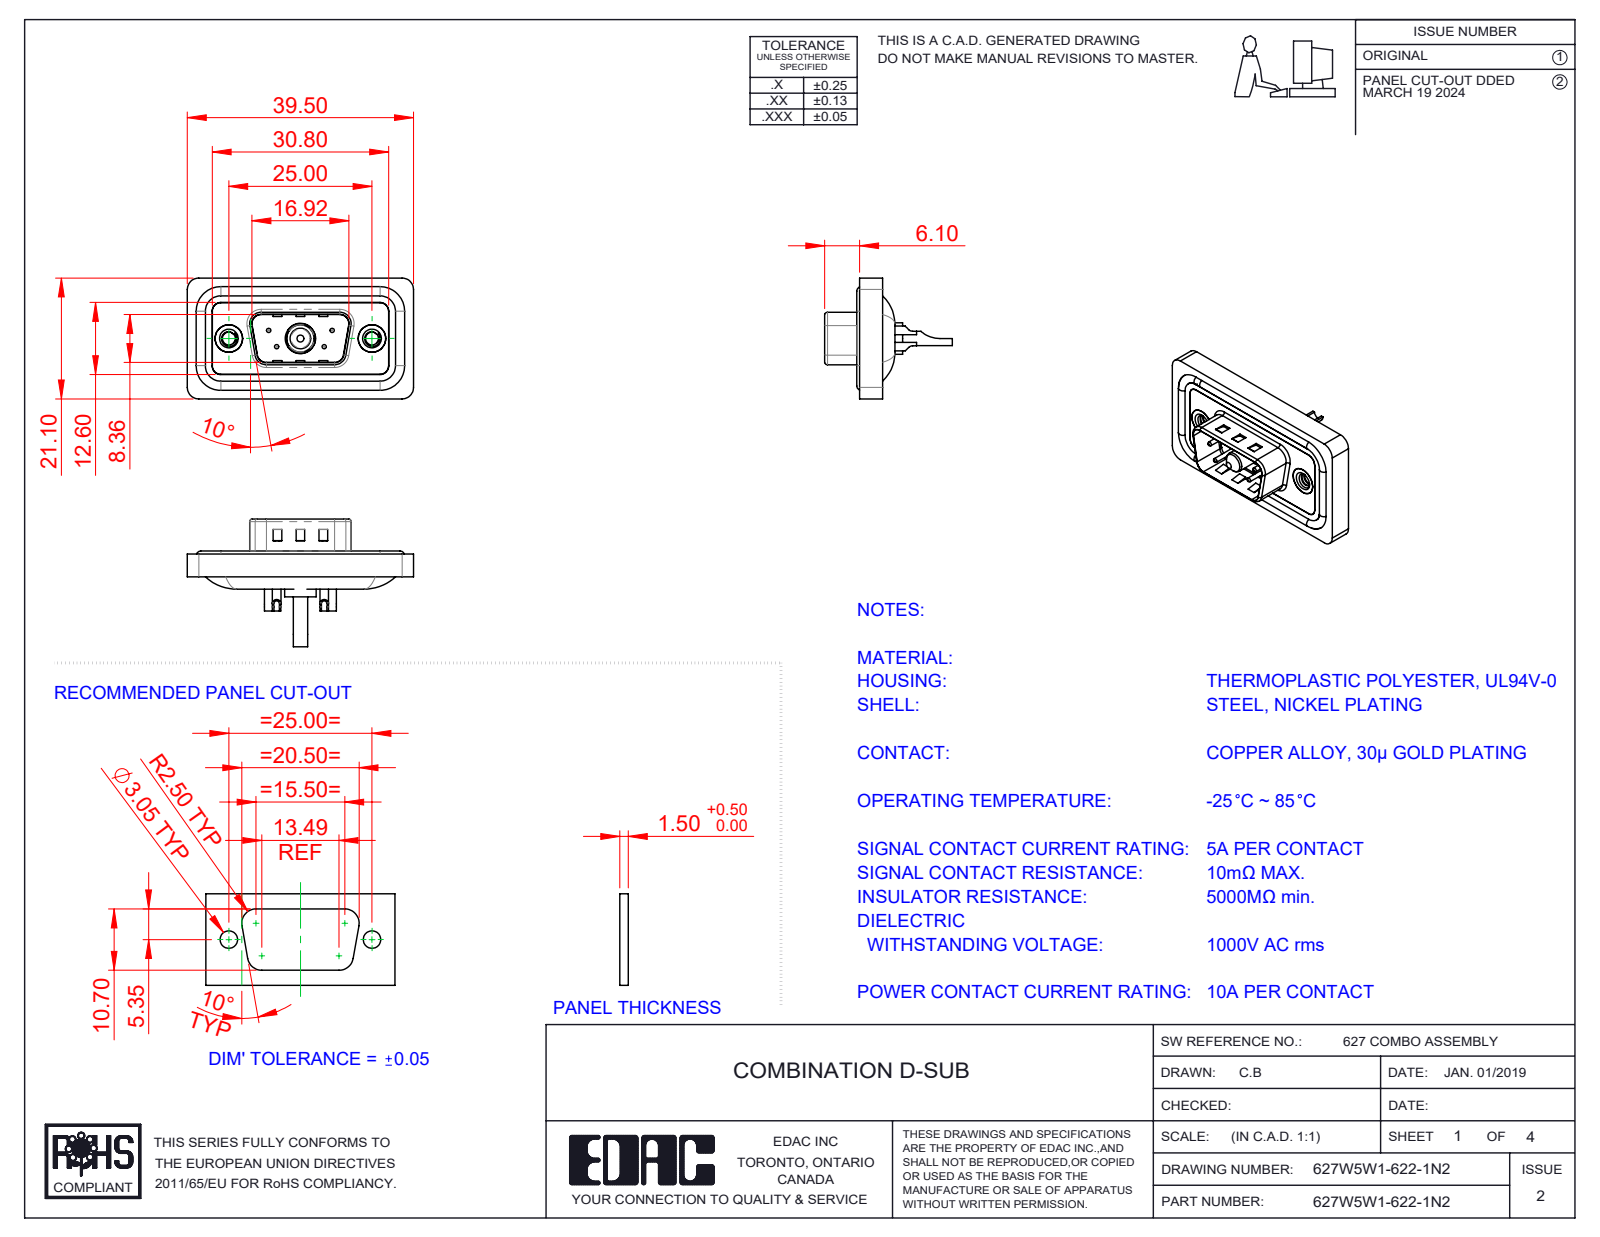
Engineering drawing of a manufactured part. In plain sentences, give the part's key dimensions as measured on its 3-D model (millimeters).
The part is named "627W5W1-622-1N2; Power Pin_10A SC; 627Combo Waterproof Housing_09 Contacts; 627Combo Threaded Rivet_2 (+5 more)". Its 3-D file was written by "SolidWorks 2023 (CONFIG_CONTROL_DESIGN)". It is 13 solids with 604 faces: 193 planar, 266 cylindrical and 145 other. Overall it measures 39.5 by 22.3 by 21.1 millimeters. Its volume is 4 391 cubic millimeters and its surface area 7 021 square millimeters. Round holes: 4 of diameter 0.75, 4 of diameter 1, 4 of diameter 1.6, 4 of diameter 2, 2 of diameter 2.26, 2 of diameter 4, 2 of diameter 4.8, 2 of diameter 5, 1 of diameter 1.7, 1 of diameter 4.85, 1 of diameter 5.3. Round bosses or shafts: 4 of diameter 1.6, 4 of diameter 1.5, 2 of diameter 4.9, 1 of diameter 5.5, 1 of diameter 5.2, 1 of diameter 4.75, 1 of diameter 3.75, 1 of diameter 3.6. Partial cylindrical surfaces (rounded edges, fillets, slot ends): 22 of radius 1.5, 18 of radius 2, 8 of radius 0.5, 8 of radius 1.6, 6 of radius 1, 4 of radius 0.25, 4 of radius 0.6, 4 of radius 0.65. The main face-to-face distances are 0.4, 1.1, 2.9, 1.6, 1.5, 3.1, 0.5, 2.5, 4, 0.8. The hole center spacings are 3.16, 5.72, 7.1, 12.5, 18.1, 4.39, 4.4, 8.31.
